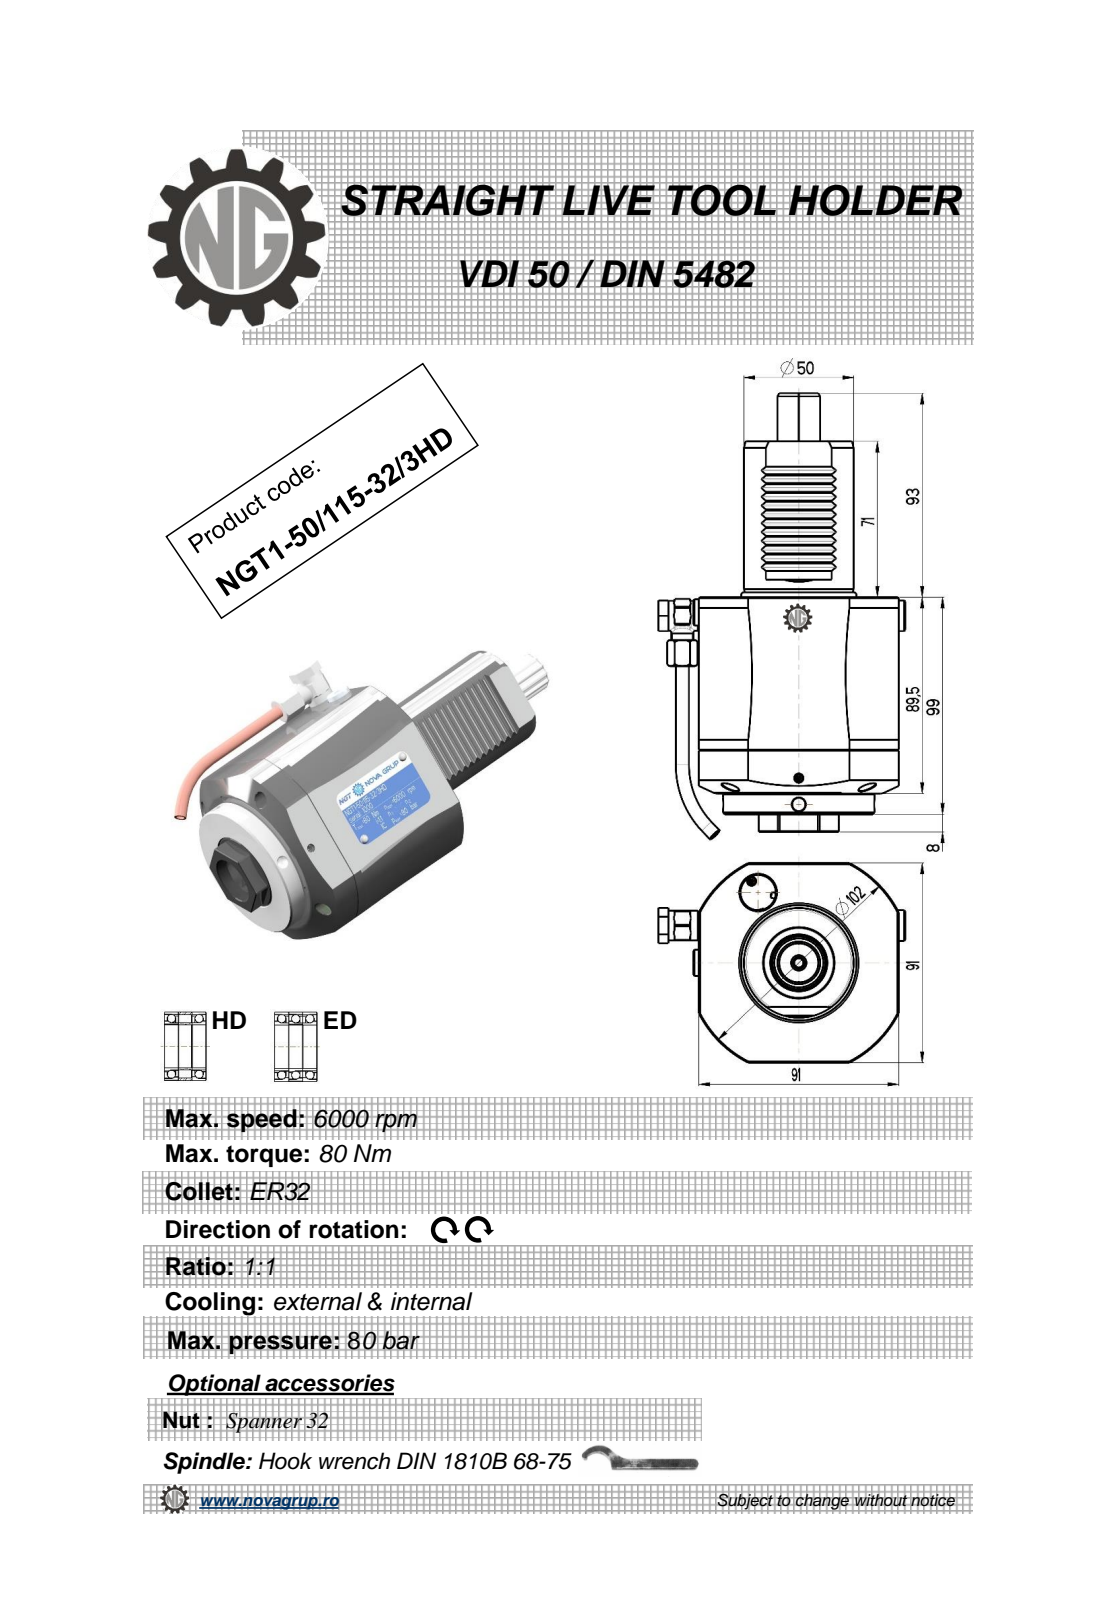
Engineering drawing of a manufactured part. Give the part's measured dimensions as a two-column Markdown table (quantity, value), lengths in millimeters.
| quantity | value |
| --- | --- |
| part name | NGT1_50_115_32_3HD |
| STEP written by | PRO/ENGINEER BY PARAMETRIC TECHNOLOGY CORPORATION, 2010280 (CONFIG_CONTROL_DESIGN) |
| units | millimeters |
| bodies | 1 solid, 428 faces (142 planar, 148 cylindrical, 138 other) |
| overall size | 203.44 × 112.4 × 91 |
| volume | 832 732 mm³ |
| surface area | 66 568 mm² |
| round holes (diameter × count) | 4 × 3, 6 × 2, 3 × 1, 4.2 × 1, 5.3 × 1, 6.2 × 1, 9 × 1, 10 × 1, 11 × 1, 23 × 1, 34 × 1 |
| round bosses / shafts (diameter × count) | 6 × 2, 69 × 1, 50 × 1, 14 × 1, 13.6 × 1, 13 × 1, 12 × 1, 10 × 1 |
| partial cylindrical surfaces (radius × count) | 3.33 × 24, 0.3 × 12, 0.41 × 6, 0.5 × 4, 20 × 2, 6.25 × 1, 7.7 × 1, 8.64 × 1 |
| main face-to-face distances | 91, 99, 9.5, 89.5, 170, 160.5, 71, 2.83, 14.14, 11.31 |
| hole center spacings | 0.4, 55.66, 56.04, 87.66 |
